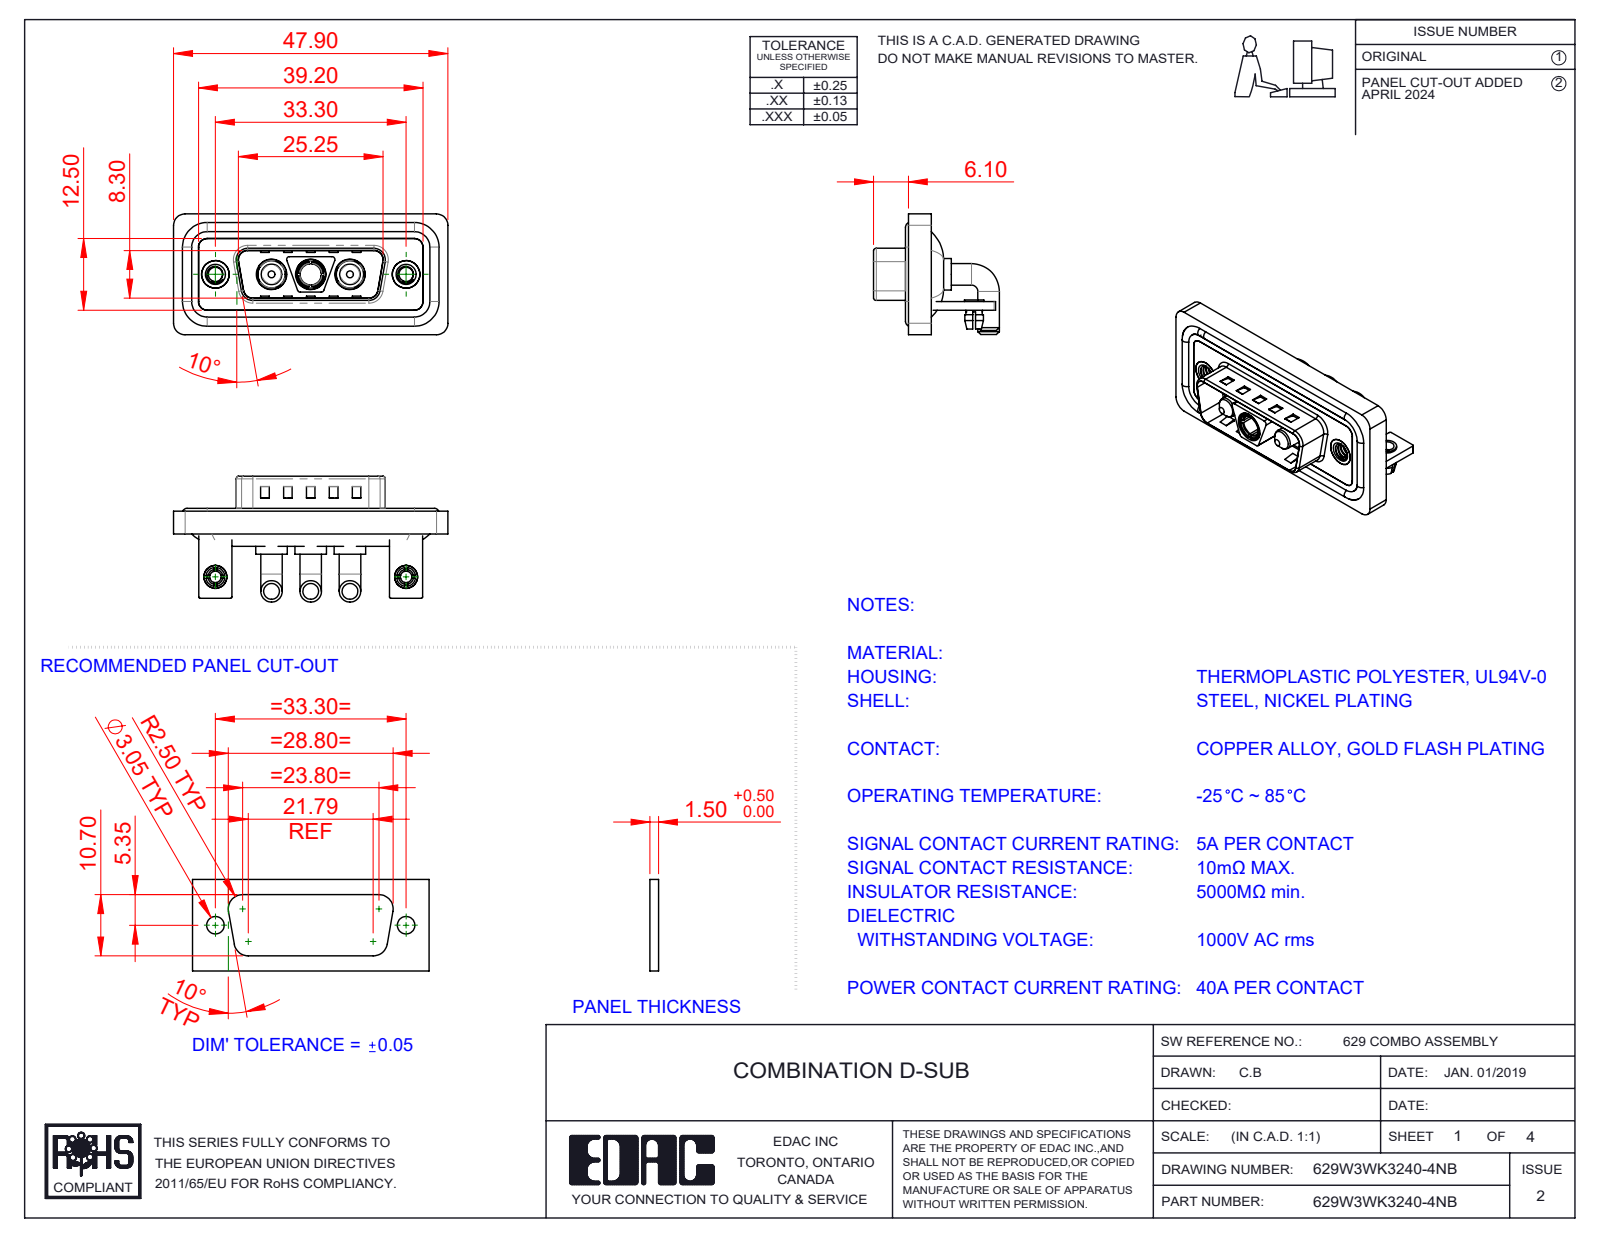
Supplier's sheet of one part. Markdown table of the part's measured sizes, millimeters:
| quantity | value |
| --- | --- |
| part name | 629Combo Shell Front_15 Contacts; 629Combo Housing_3WK3; 629Combo Waterproof Housing_15 Contacts; Power Pin_40A RA (+6 more) |
| STEP written by | SolidWorks 2023 (CONFIG_CONTROL_DESIGN) |
| units | millimeters |
| bodies | 17 solids, 751 faces (299 planar, 306 cylindrical, 146 other) |
| overall size | 47.9 × 21.98 × 21.1 |
| volume | 6 415 mm³ |
| surface area | 10 348 mm² |
| round holes (diameter × count) | 2.5 × 4, 4.85 × 3, 5.3 × 3, 2 × 2, 3.2 × 2, 4 × 2, 4.8 × 2, 5 × 2, 3.7 × 1 |
| round bosses / shafts (diameter × count) | 3.75 × 6, 1.6 × 4, 5.5 × 3, 5.2 × 3, 4.75 × 3, 4.9 × 2, 4 × 2, 3.6 × 2 |
| partial cylindrical surfaces (radius × count) | 2 × 21, 1.5 × 18, 0.25 × 16, 0.5 × 13, 1.6 × 8, 0.6 × 4, 0.65 × 4, 0.9 × 4 |
| main face-to-face distances | 0.4, 1.5, 0.8, 2.9, 1.1, 2.1, 3.7, 1.6, 1.2, 4.5 |
| hole center spacings | 6.85, 9.8, 16.65, 23.5, 33.3, 13.7 |
